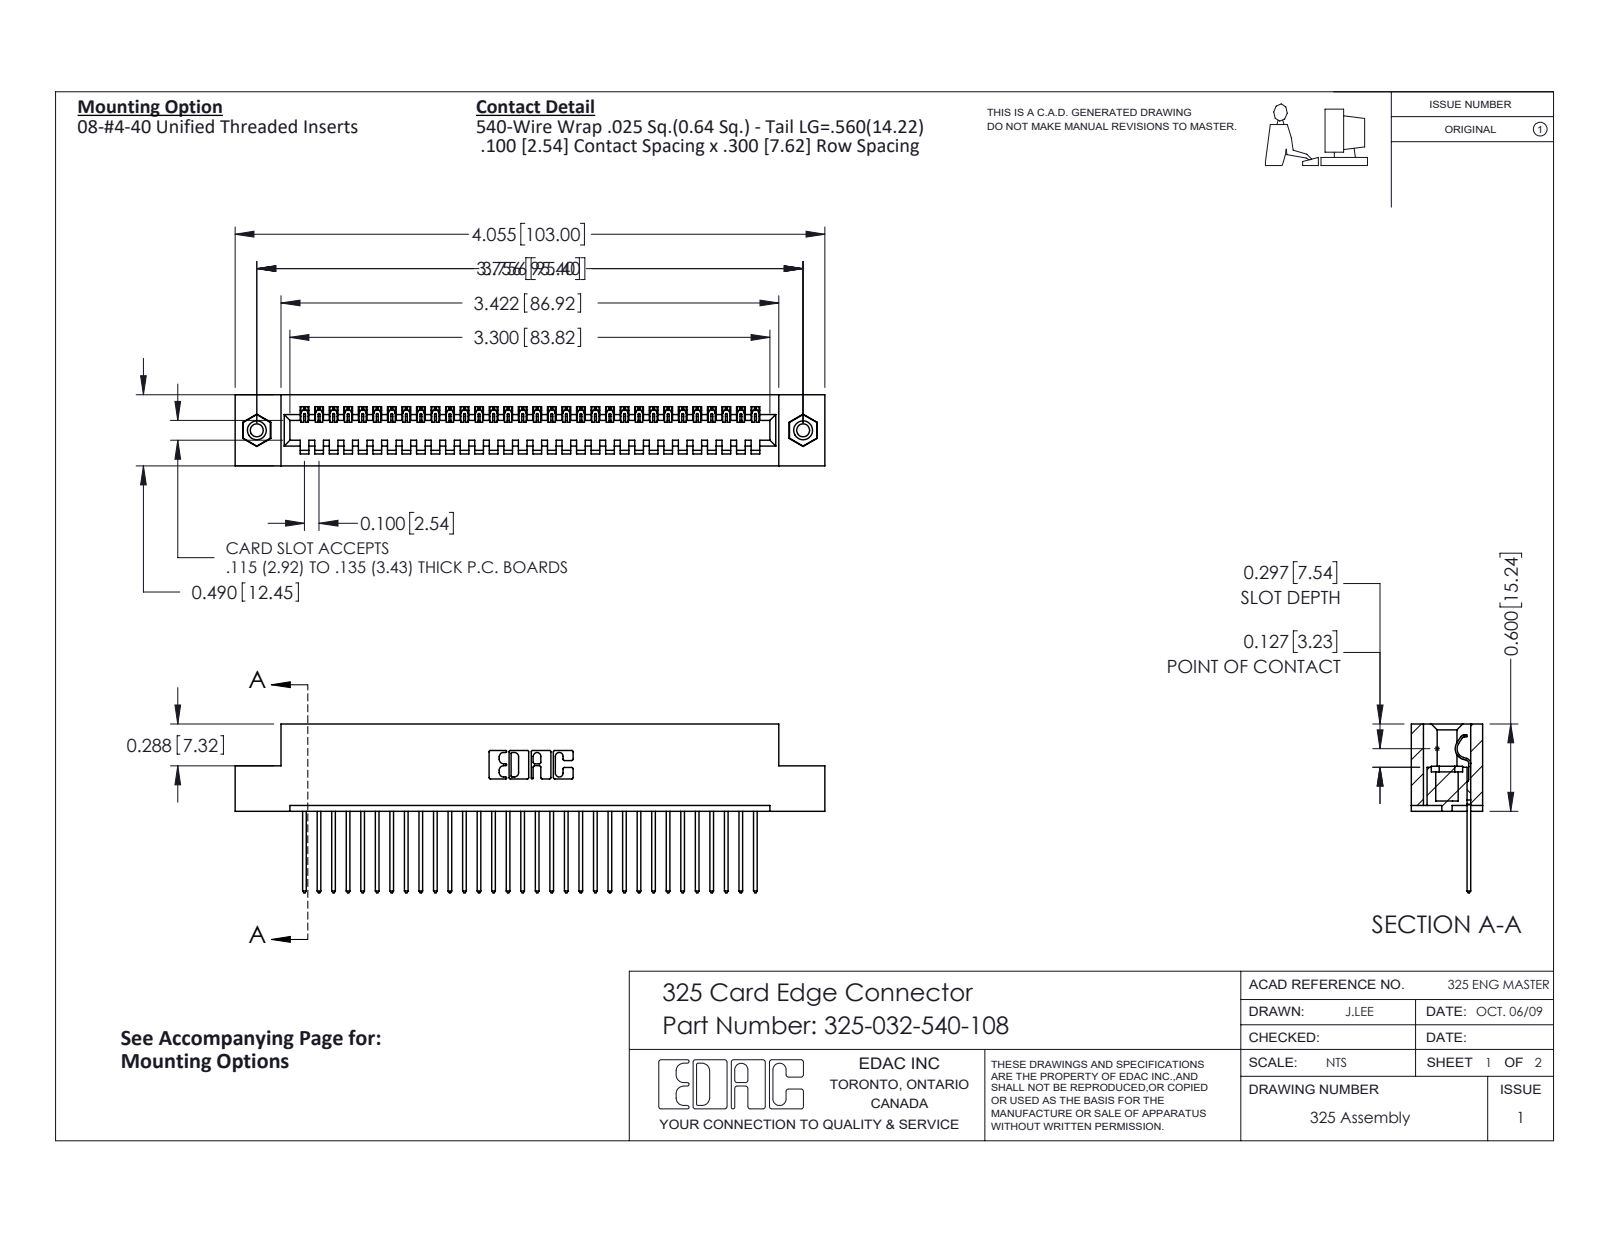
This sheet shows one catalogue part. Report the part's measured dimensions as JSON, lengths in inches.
{"part_name": "325 Part_TI; 325-032-540-108; 325-292-001_325-293-140; 345-250-001_345-250-003-102", "step_written_by": "SolidWorks 2016 (CONFIG_CONTROL_DESIGN)", "units": "inches", "bodies": {"solids": 35, "faces": 2030, "planar": 1446, "cylindrical": 568, "other": 16}, "overall_size": [4.055, 1.16, 0.49], "volume_in3": 0.795, "surface_area_in2": 22.33, "round_holes": [[0.089, 2], [0.125, 2], [0.16, 2]], "round_bosses_or_shafts": [[0.155, 2]], "partial_cylinders_radius": [[0.006, 64], [0.01, 64], [0.01, 22], [0.007, 6], [0.031, 6], [0.026, 3], [0.014, 1], [0.022, 1]], "face_to_face_distances": [0.083, 0.407, 0.3, 0.49, 0.107, 0.383, 0.025, 0.325, 0.04, 0.1], "hole_center_spacings": [3.756]}
